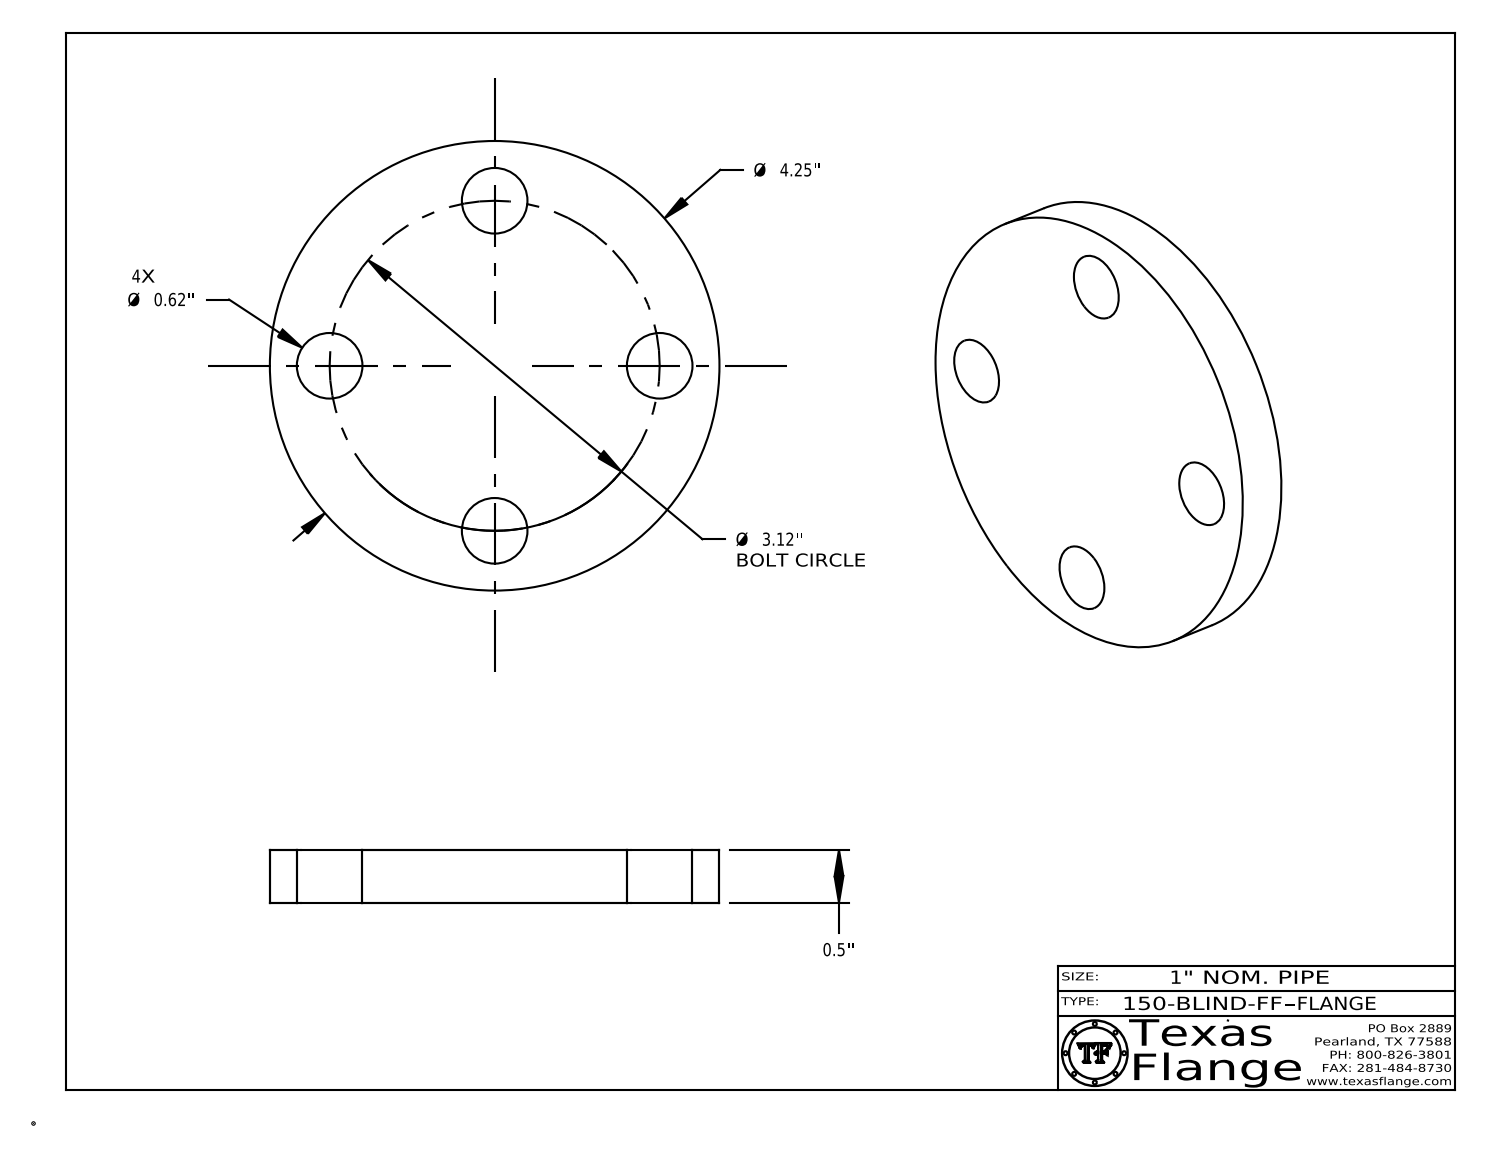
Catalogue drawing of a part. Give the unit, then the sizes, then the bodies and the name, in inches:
Units: inches
Overall size (bounding box): 4.25 × 4.25 × 0.5
Round holes (diameter × count): ⌀0.62 ×4, ⌀0.495 ×1
Round bosses / shafts (diameter × count): ⌀0.03 ×8, ⌀4.25 ×1, ⌀0.39 ×1
Main face-to-face distances: 0.5, 0.485, 0.015, 0.148, 0.144, 0.027, 0.122, 0.096, 0.021, 0.101
Hole centre spacings: 2.206, 1.194, 2.882, 3.12
Volume: 6.488 in³ · Surface area: 36.62 in²
Bodies: 1 solid, 397 faces (367 planar, 30 cylindrical, 0 other)
Part name (STEP PRODUCT): 150-BLIND-FF
STEP written by: CATIA V5 STEP AP214 (AUTOMOTIVE_DESIGN)
